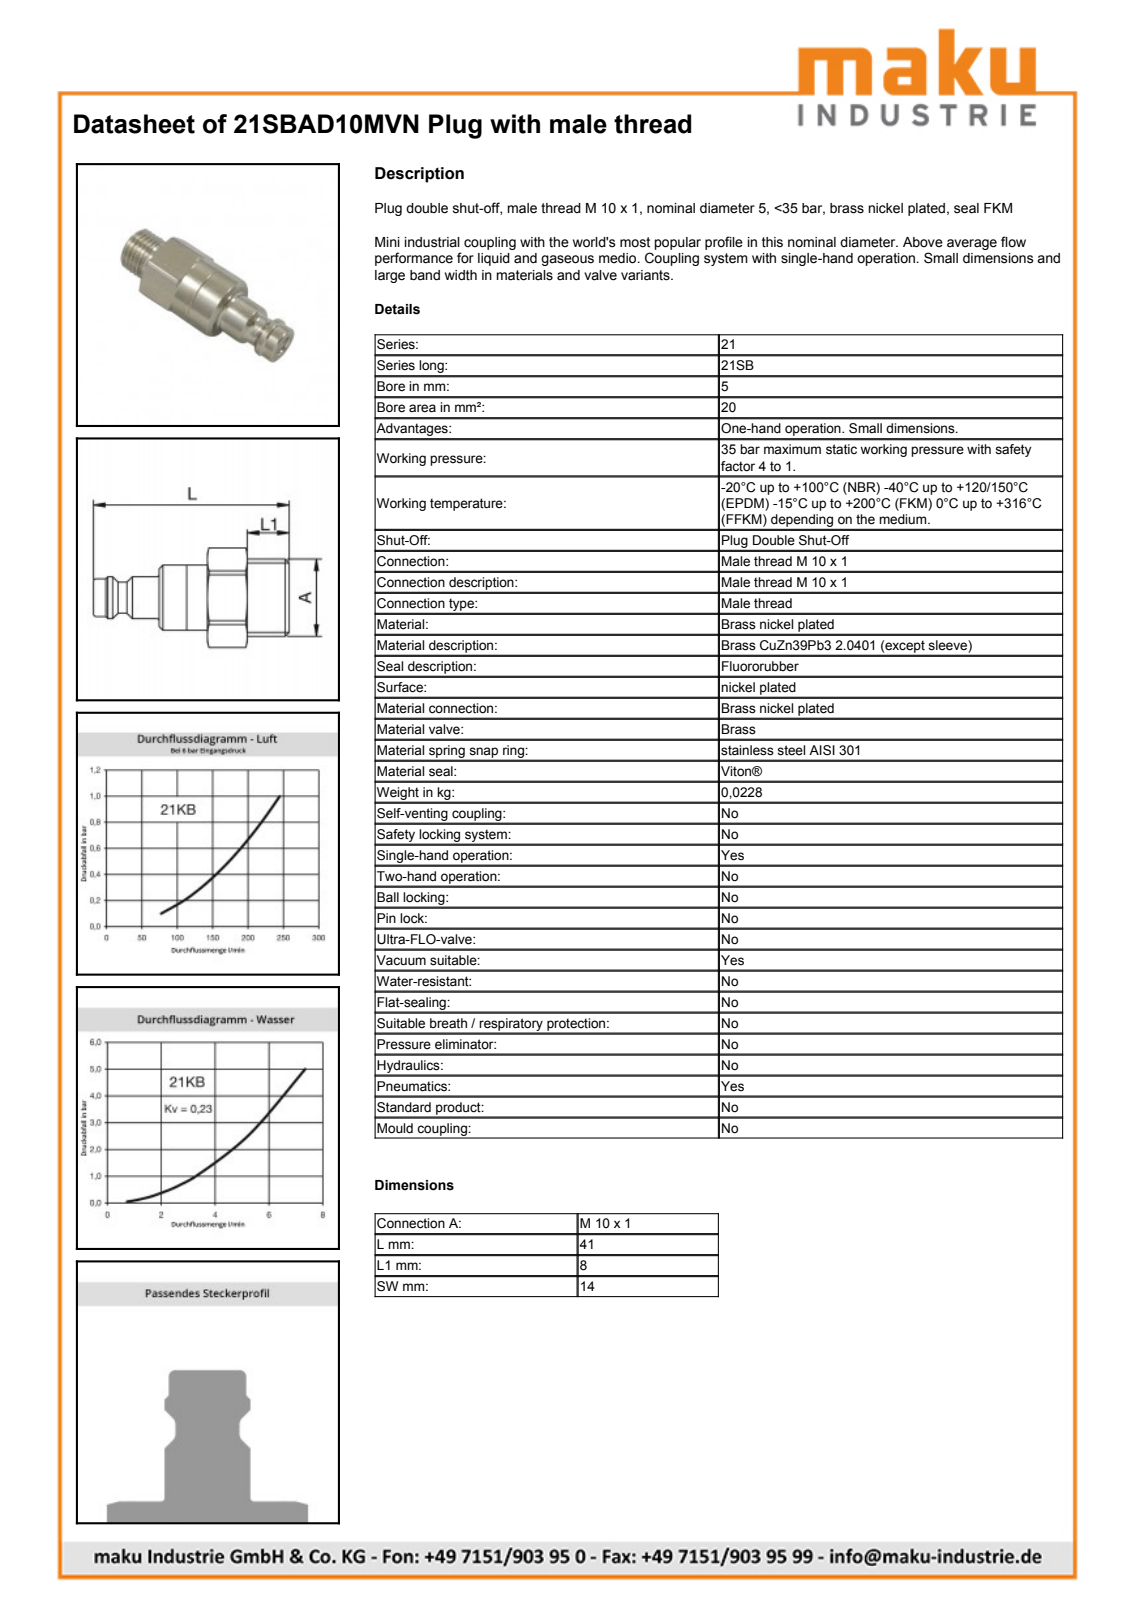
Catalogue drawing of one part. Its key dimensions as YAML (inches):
part_name: "D107383"
step_written_by: "Autodesk Inventor 2013 (AUTOMOTIVE_DESIGN)"
units: inches
bodies: {solids: 1, faces: 57, planar: 11, cylindrical: 17, other: 29}
overall_size: [1.614, 0.615, 0.596]
volume: 0.267
surface_area: 3.1
round_holes:
  - {diameter: 0.453, count: 1}
round_bosses_or_shafts:
  - {diameter: 0.551, count: 1}
  - {diameter: 0.449, count: 1}
  - {diameter: 0.394, count: 1}
  - {diameter: 0.354, count: 1}
  - {diameter: 0.335, count: 1}
  - {diameter: 0.319, count: 1}
  - {diameter: 0.262, count: 1}
partial_cylinders:
  - {radius: 0.311, count: 1}
face_to_face_distances: [0.551, 0.315, 0.744, 1.059, 0.555, 1.299, 1.614, 0.787, 0.232, 0.512]
